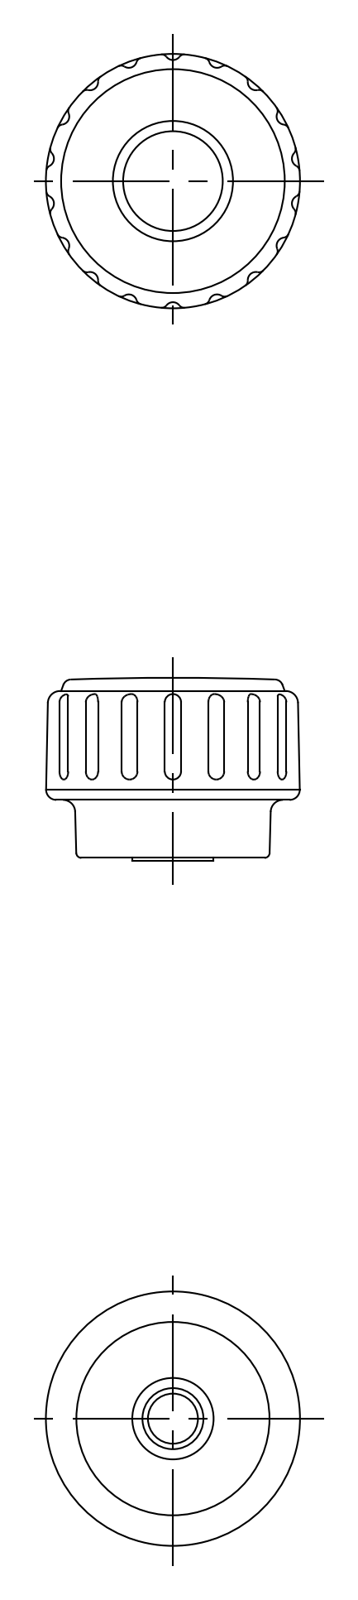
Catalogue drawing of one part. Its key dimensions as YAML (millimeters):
part_name: "screw; knob; KDFS_25_M6_WH_22923_36"
step_written_by: "CADfix (AUTOMOTIVE_DESIGN)"
units: millimeters
bodies: {solids: 2, faces: 107, planar: 0, cylindrical: 0, other: 107}
overall_size: [24.96, 24.96, 17.94]
volume: 6795
surface_area: 2785
